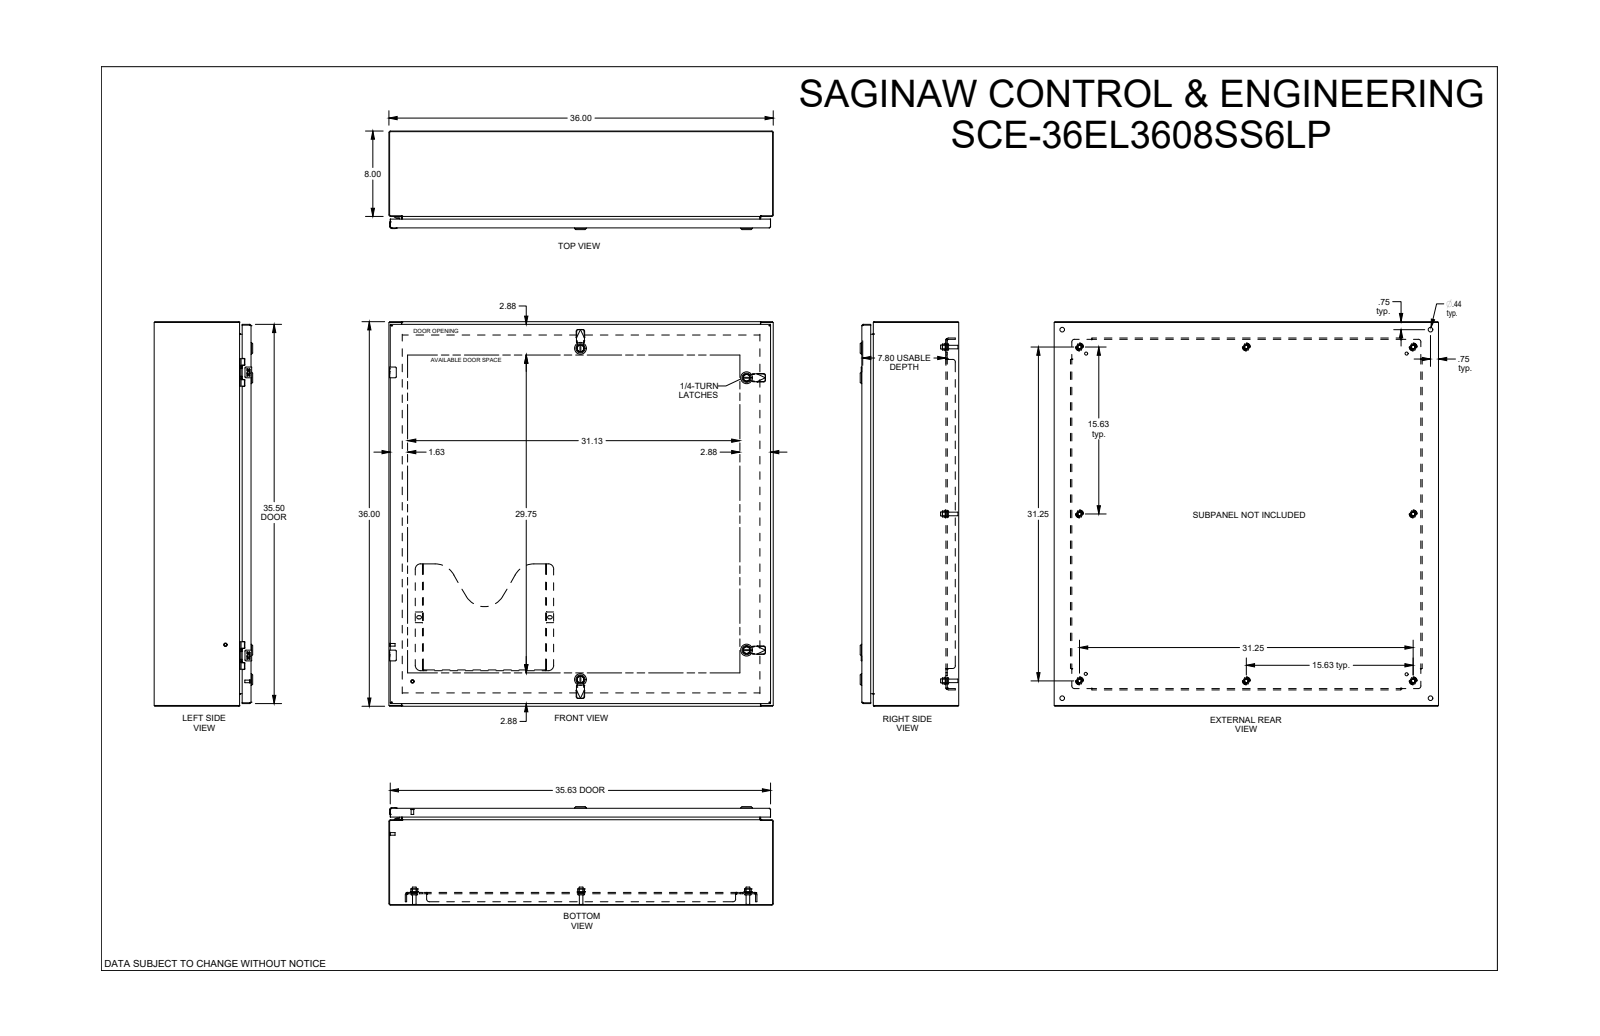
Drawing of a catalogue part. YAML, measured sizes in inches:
part_name: "SCE-36EL3608SS6LP"
step_written_by: "SolidWorks 2019 (CONFIG_CONTROL_DESIGN)"
units: inches
bodies: {solids: 0, faces: 3904, planar: 1851, cylindrical: 1049, other: 1004}
overall_size: [36, 36, 9.23]
round_holes:
  - {diameter: 0.367, count: 8}
  - {diameter: 0.5, count: 8}
  - {diameter: 0.172, count: 4}
  - {diameter: 0.197, count: 4}
  - {diameter: 0.205, count: 4}
  - {diameter: 0.244, count: 4}
  - {diameter: 0.266, count: 4}
  - {diameter: 0.281, count: 4}
  - {diameter: 0.315, count: 4}
  - {diameter: 0.375, count: 4}
  - {diameter: 0.394, count: 4}
  - {diameter: 0.437, count: 4}
round_bosses_or_shafts:
  - {diameter: 0.366, count: 8}
  - {diameter: 0.332, count: 8}
  - {diameter: 0.17, count: 6}
  - {diameter: 1.102, count: 4}
  - {diameter: 0.866, count: 4}
  - {diameter: 0.802, count: 4}
  - {diameter: 0.78, count: 4}
  - {diameter: 0.63, count: 4}
partial_cylinders:
  - {radius: 0.012, count: 116}
  - {radius: 0.01, count: 52}
  - {radius: 0.02, count: 44}
  - {radius: 0.015, count: 28}
  - {radius: 0.04, count: 23}
  - {radius: 0.157, count: 16}
  - {radius: 0.07, count: 14}
  - {radius: 0.029, count: 12}
face_to_face_distances: [0.075, 0.075, 8.923, 8.998, 9.073, 8.998, 1.2, 7.873, 35.925, 1]
hole_center_spacings: [15.625, 17.326, 26.5, 32.915, 34.939, 37.126, 0.985, 15.019]
